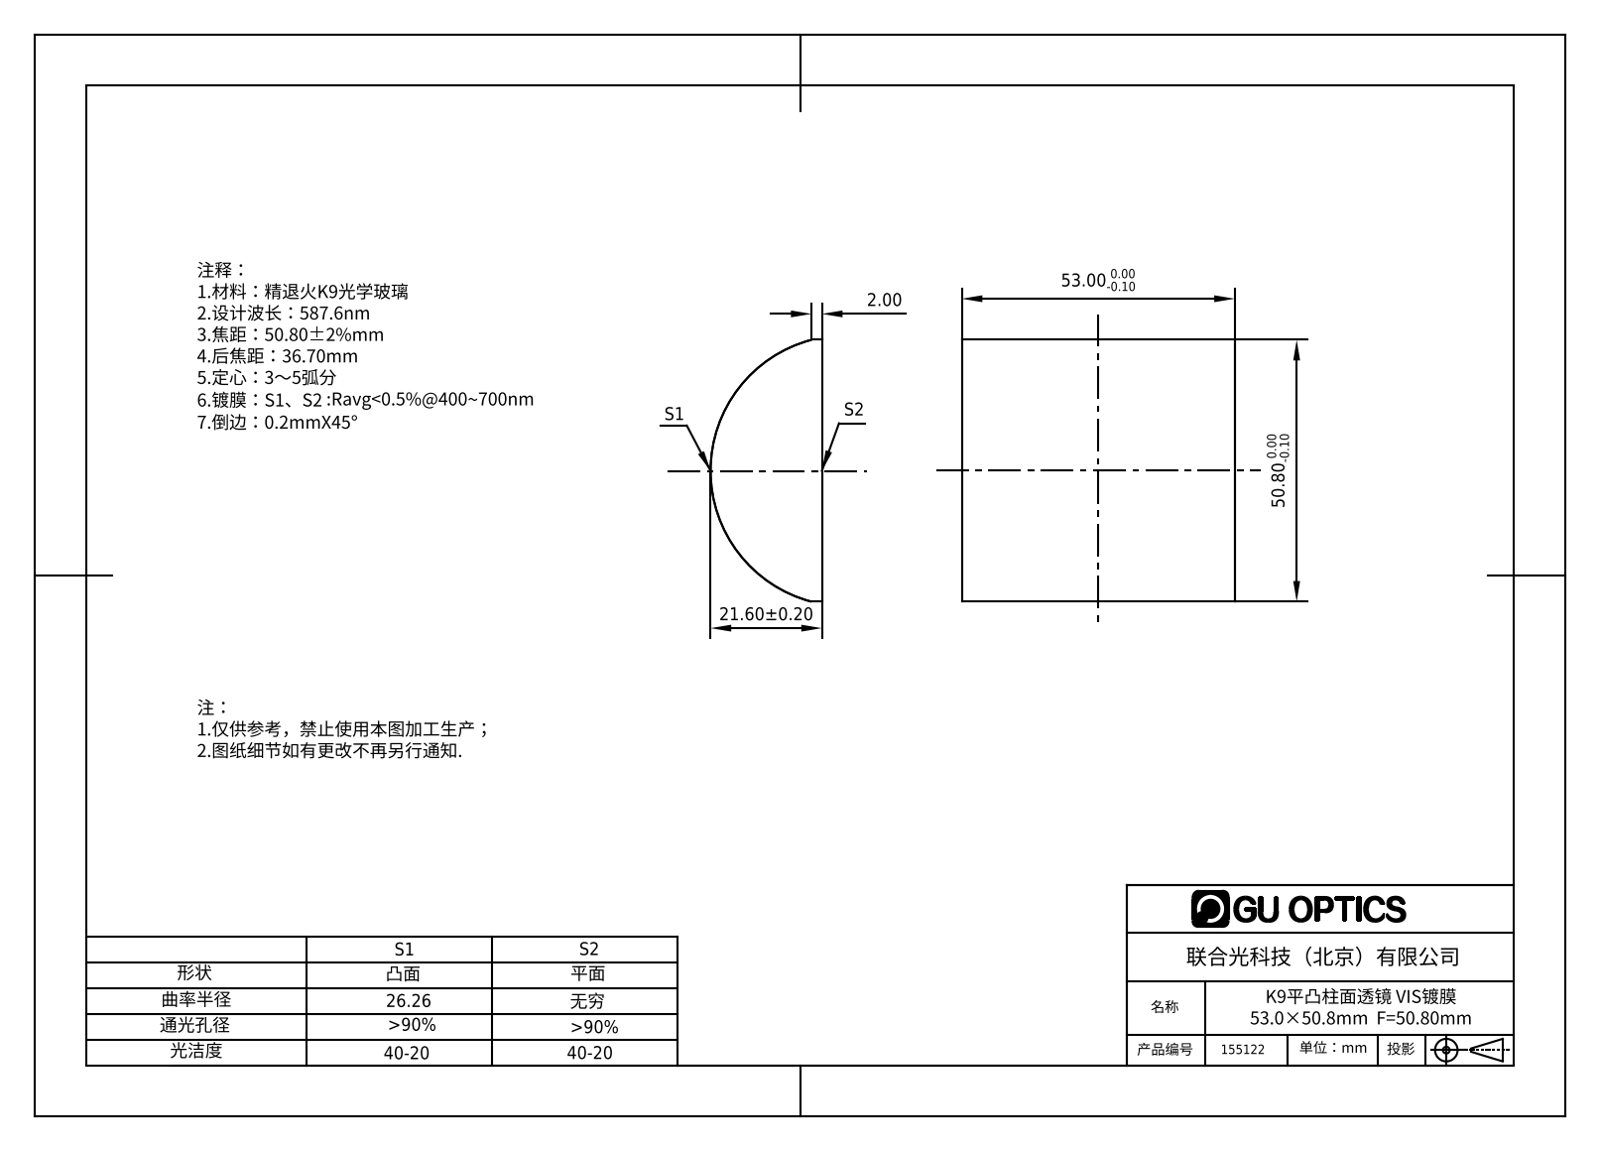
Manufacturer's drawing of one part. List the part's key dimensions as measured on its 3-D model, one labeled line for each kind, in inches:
Part name (STEP PRODUCT): 155056
STEP written by: SolidWorks 2016 (AUTOMOTIVE_DESIGN)
Units: inches
Bodies: 1 solid, 6 faces (5 planar, 1 cylindrical, 0 other)
Overall size (bounding box): 2.087 × 2 × 0.85
Volume: 2.713 in³ · Surface area: 12.77 in²
Partial cylindrical surfaces — rounded edges, fillets, slot ends (radius × count): R1.034 ×1
Main face-to-face distances: 2.087, 2
